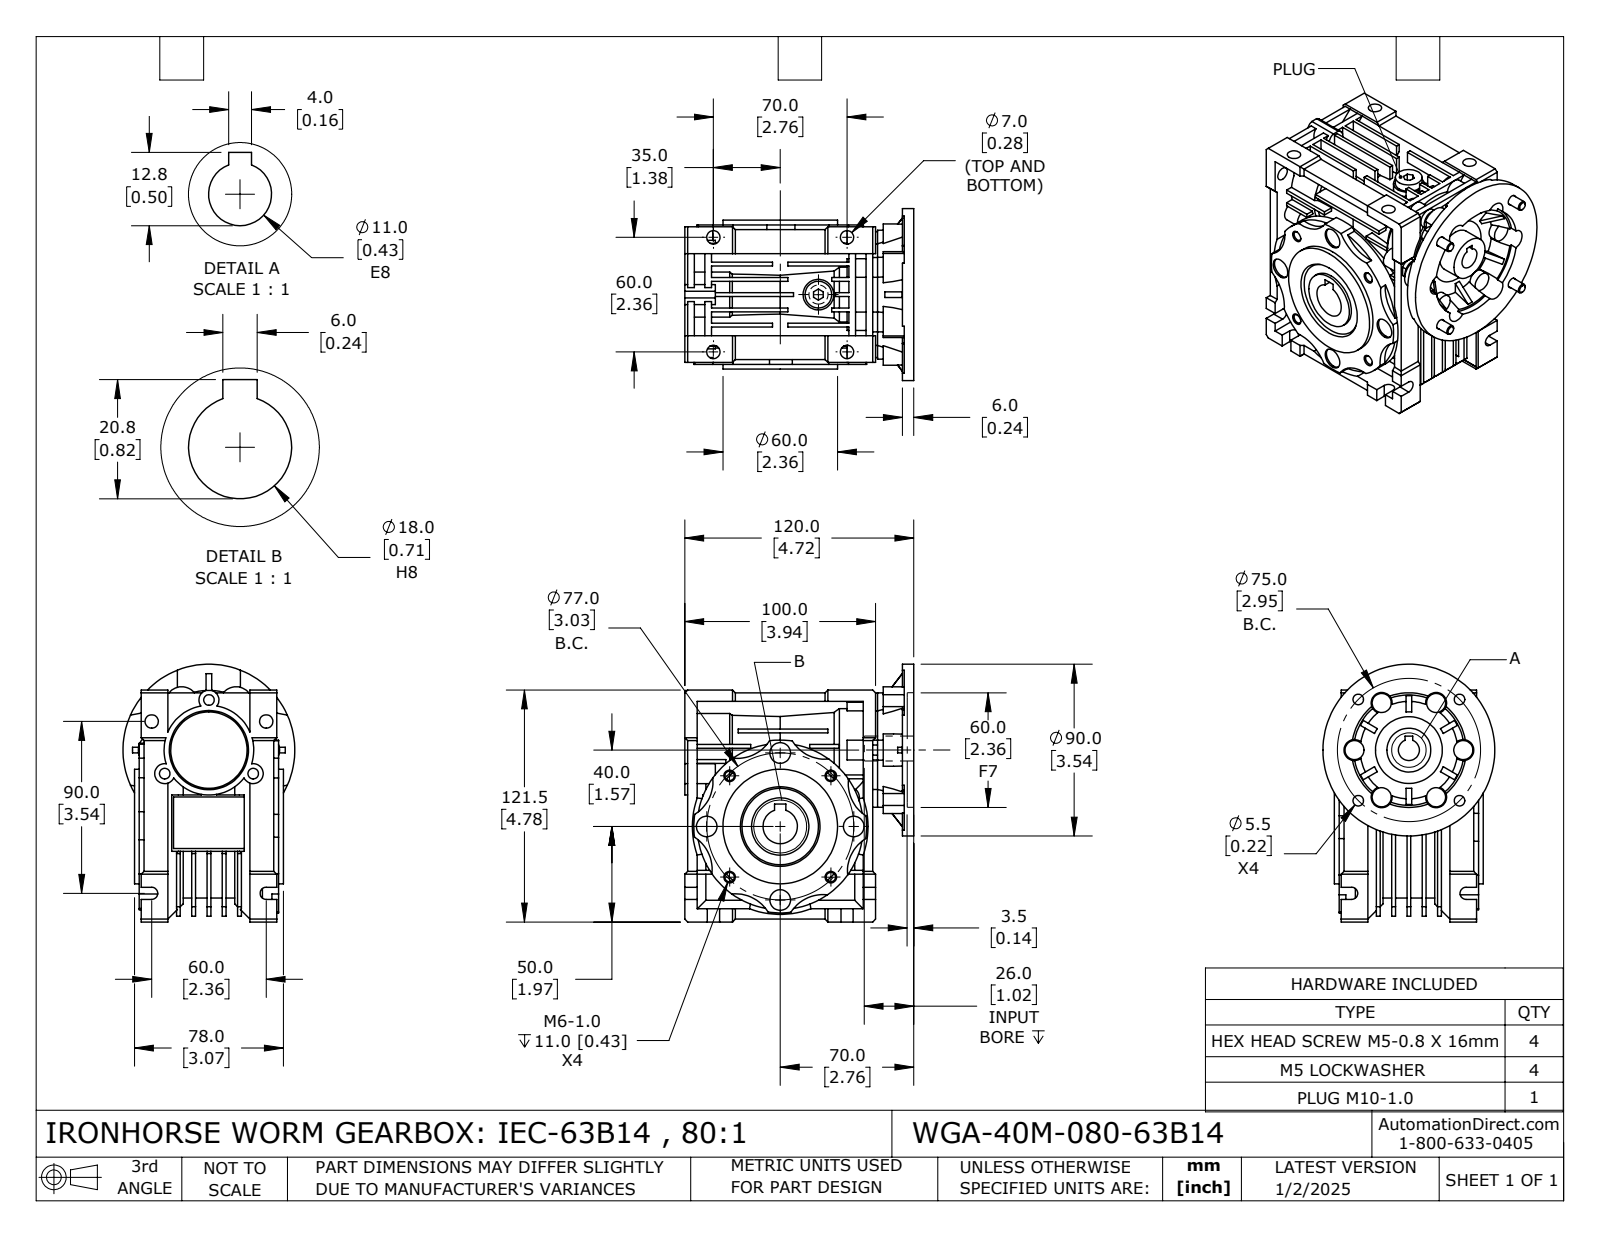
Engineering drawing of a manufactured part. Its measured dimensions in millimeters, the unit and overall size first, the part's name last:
Units: millimetres
Overall size (bounding box): 135 × 127.7 × 90
Round holes (diameter × count): ⌀7 ×6, ⌀4.92 ×4, ⌀5.1 ×4, ⌀5.5 ×4, ⌀10.8 ×4, ⌀5.55 ×3, ⌀9 ×1, ⌀11 ×1, ⌀11.5 ×1, ⌀18 ×1, ⌀23 ×1, ⌀28 ×1
Round bosses / shafts (diameter × count): ⌀10 ×6, ⌀9.2 ×4, ⌀5 ×4, ⌀90 ×1, ⌀75 ×1, ⌀60 ×1, ⌀54 ×1, ⌀47 ×1
Partial cylindrical surfaces — rounded edges, fillets, slot ends (radius × count): R5.25 ×9, R20 ×8, R3.2 ×6, R5.22 ×6, R5.5 ×6, R8.5 ×6, R5.51 ×4, R30 ×1
Main face-to-face distances: 8, 6, 2, 1.5, 16, 10, 5, 14, 2.5, 19
Hole centre spacings: 29.1, 37.5, 53.04, 70.22, 33.54, 38.5, 54.45, 75.01
Volume: 667 307 mm³ · Surface area: 163 100 mm²
Bodies: 14 solids, 1003 faces (564 planar, 307 cylindrical, 132 other)
Part name (STEP PRODUCT): WGA-40M-080-63B14
STEP written by: SolidWorks 2024 (CONFIG_CONTROL_DESIGN)
